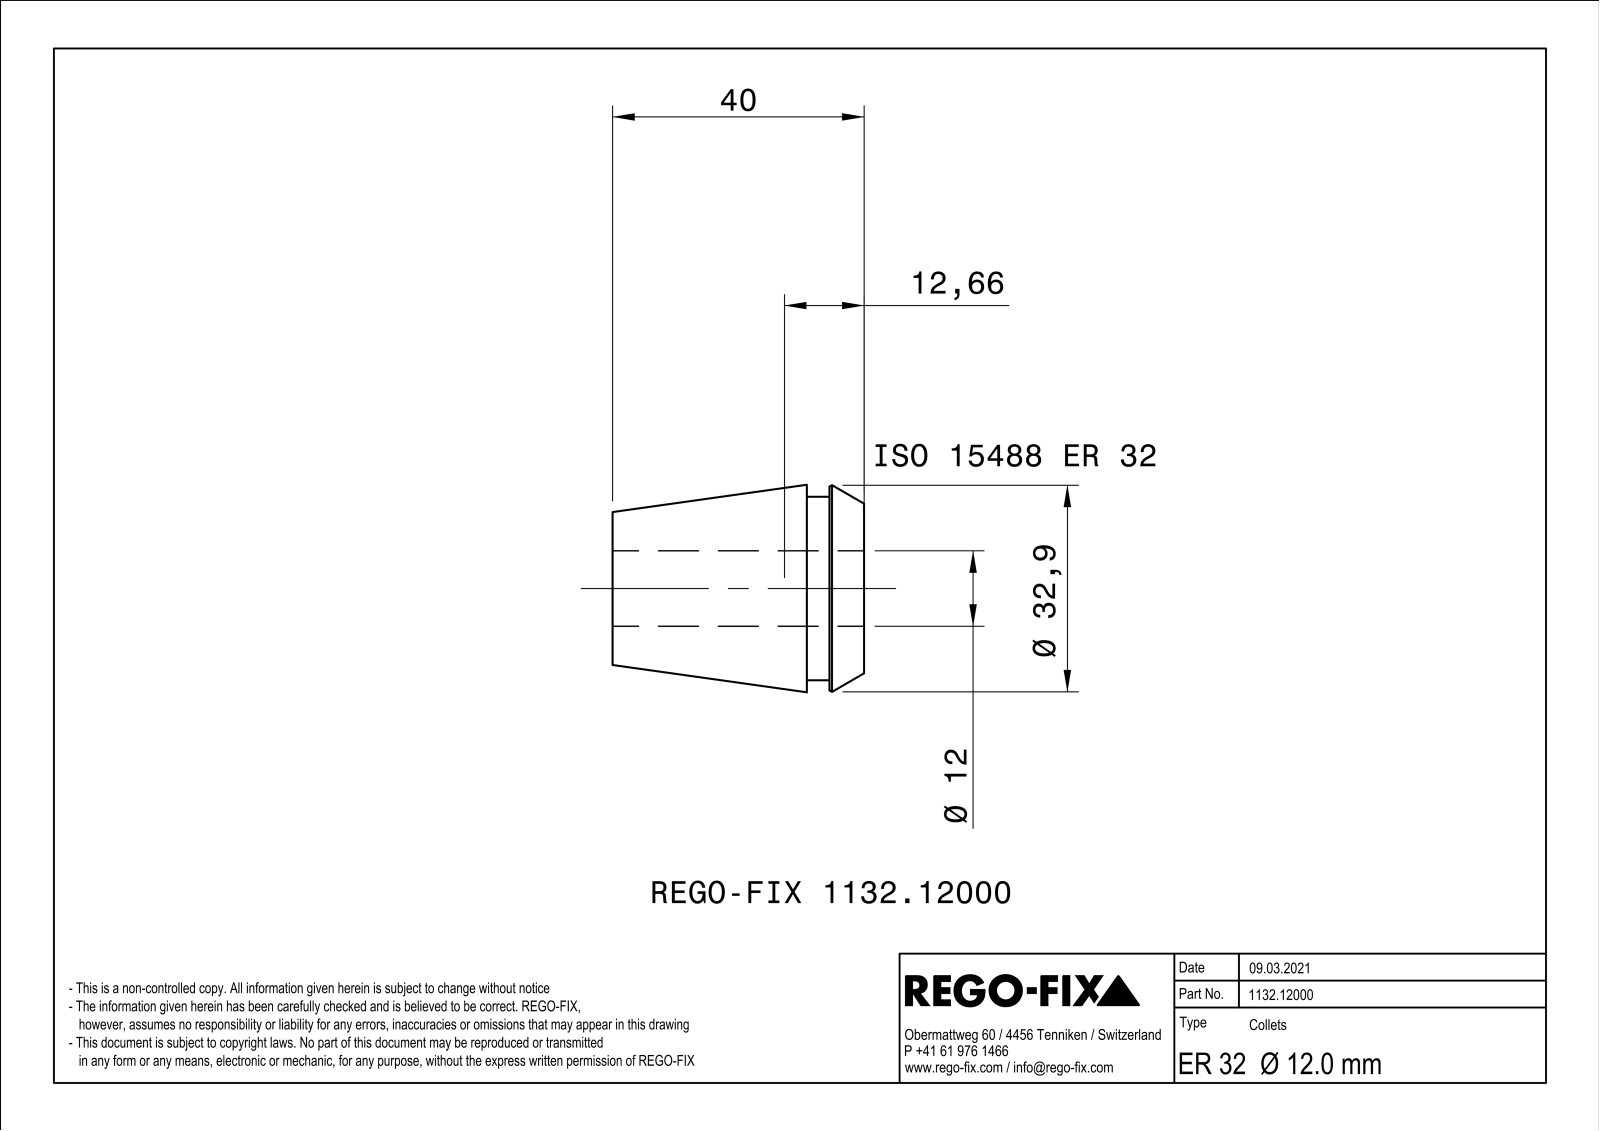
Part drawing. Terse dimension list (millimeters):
name: NOCUT
written by: SIEMENS PLM Software Solid Edge ST10 (AUTOMOTIVE_DESIGN)
unit: mm
bodies: 1 solid, 209 faces (88 planar, 41 cylindrical, 80 other)
size: 40 × 32.98 × 32.98
volume: 17 087 mm³; area: 14 819 mm²
holes: 1× ⌀12
bosses: 1× ⌀29.2
rounds: 20× R0.4
face distances: 1, 40, 9.1, 30.9, 5.5, 3.6, 34.5, 6, 0.5, 3.1
